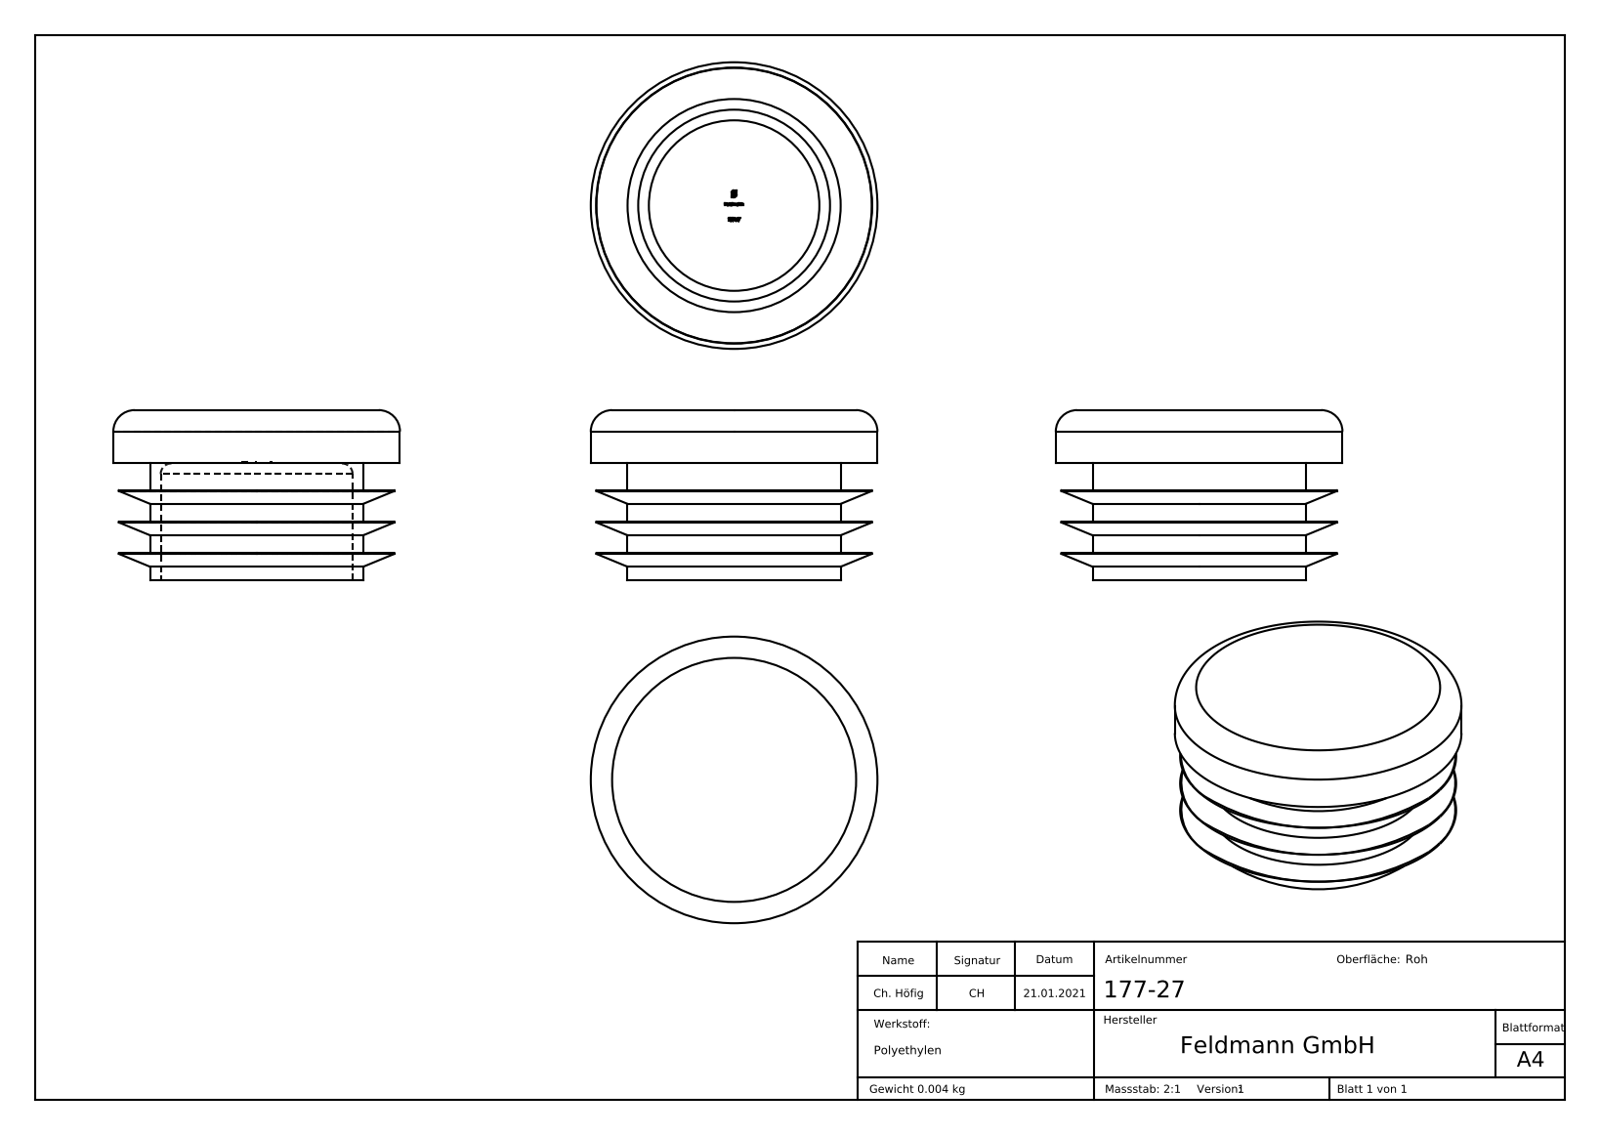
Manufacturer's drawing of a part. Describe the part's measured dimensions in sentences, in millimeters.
The part is named "177-27". Its 3-D file was written by "SolidWorks 2015 (CONFIG_CONTROL_DESIGN)". It is 1 solid with 186 faces: 112 planar, 12 cylindrical and 62 other. Overall it measures 26.9 by 26.9 by 16.5 millimeters. Its volume is 3 579 cubic millimeters and its surface area 3 859 square millimeters. Round holes: 1 of diameter 17.9. Round bosses or shafts: 1 of diameter 26.9, 1 of diameter 19.9. The main face-to-face distances are 3, 5, 6, 9, 14, 11, 8, 2.5, 5.5, 8.5.
